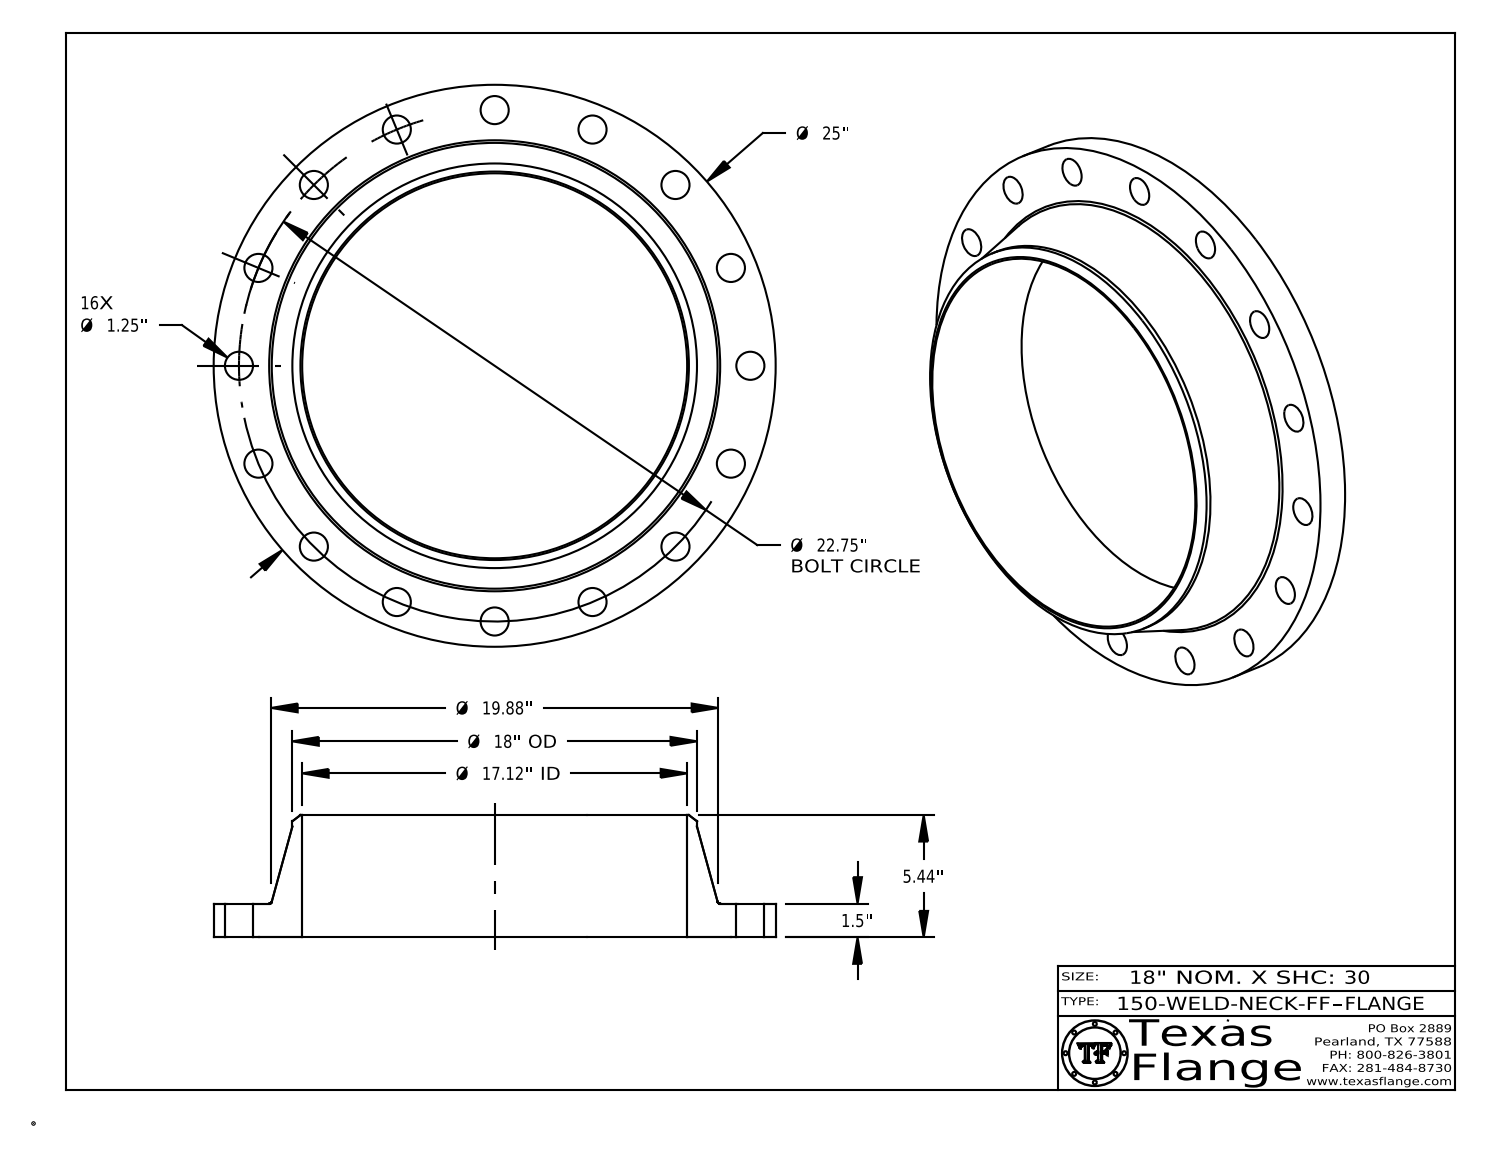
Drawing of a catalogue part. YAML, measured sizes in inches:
part_name: "150-WELD-NECK-FF"
step_written_by: "CATIA V5 STEP AP214 (AUTOMOTIVE_DESIGN)"
units: inches
bodies: {solids: 1, faces: 433, planar: 369, cylindrical: 58, other: 6}
overall_size: [25, 25, 5.44]
volume: 548.2
surface_area: 1159
round_holes:
  - {diameter: 1.25, count: 16}
  - {diameter: 0.495, count: 1}
  - {diameter: 17.124, count: 1}
round_bosses_or_shafts:
  - {diameter: 0.03, count: 8}
  - {diameter: 25, count: 1}
  - {diameter: 18, count: 1}
  - {diameter: 0.39, count: 1}
face_to_face_distances: [1.5, 5.44, 3.94, 1.485, 0.015, 3.955, 0.148, 0.145, 0.027, 0.096]
hole_center_spacings: [12.639, 22.313, 11.375, 8.706, 16.087, 21.019, 4.438, 4.439]
